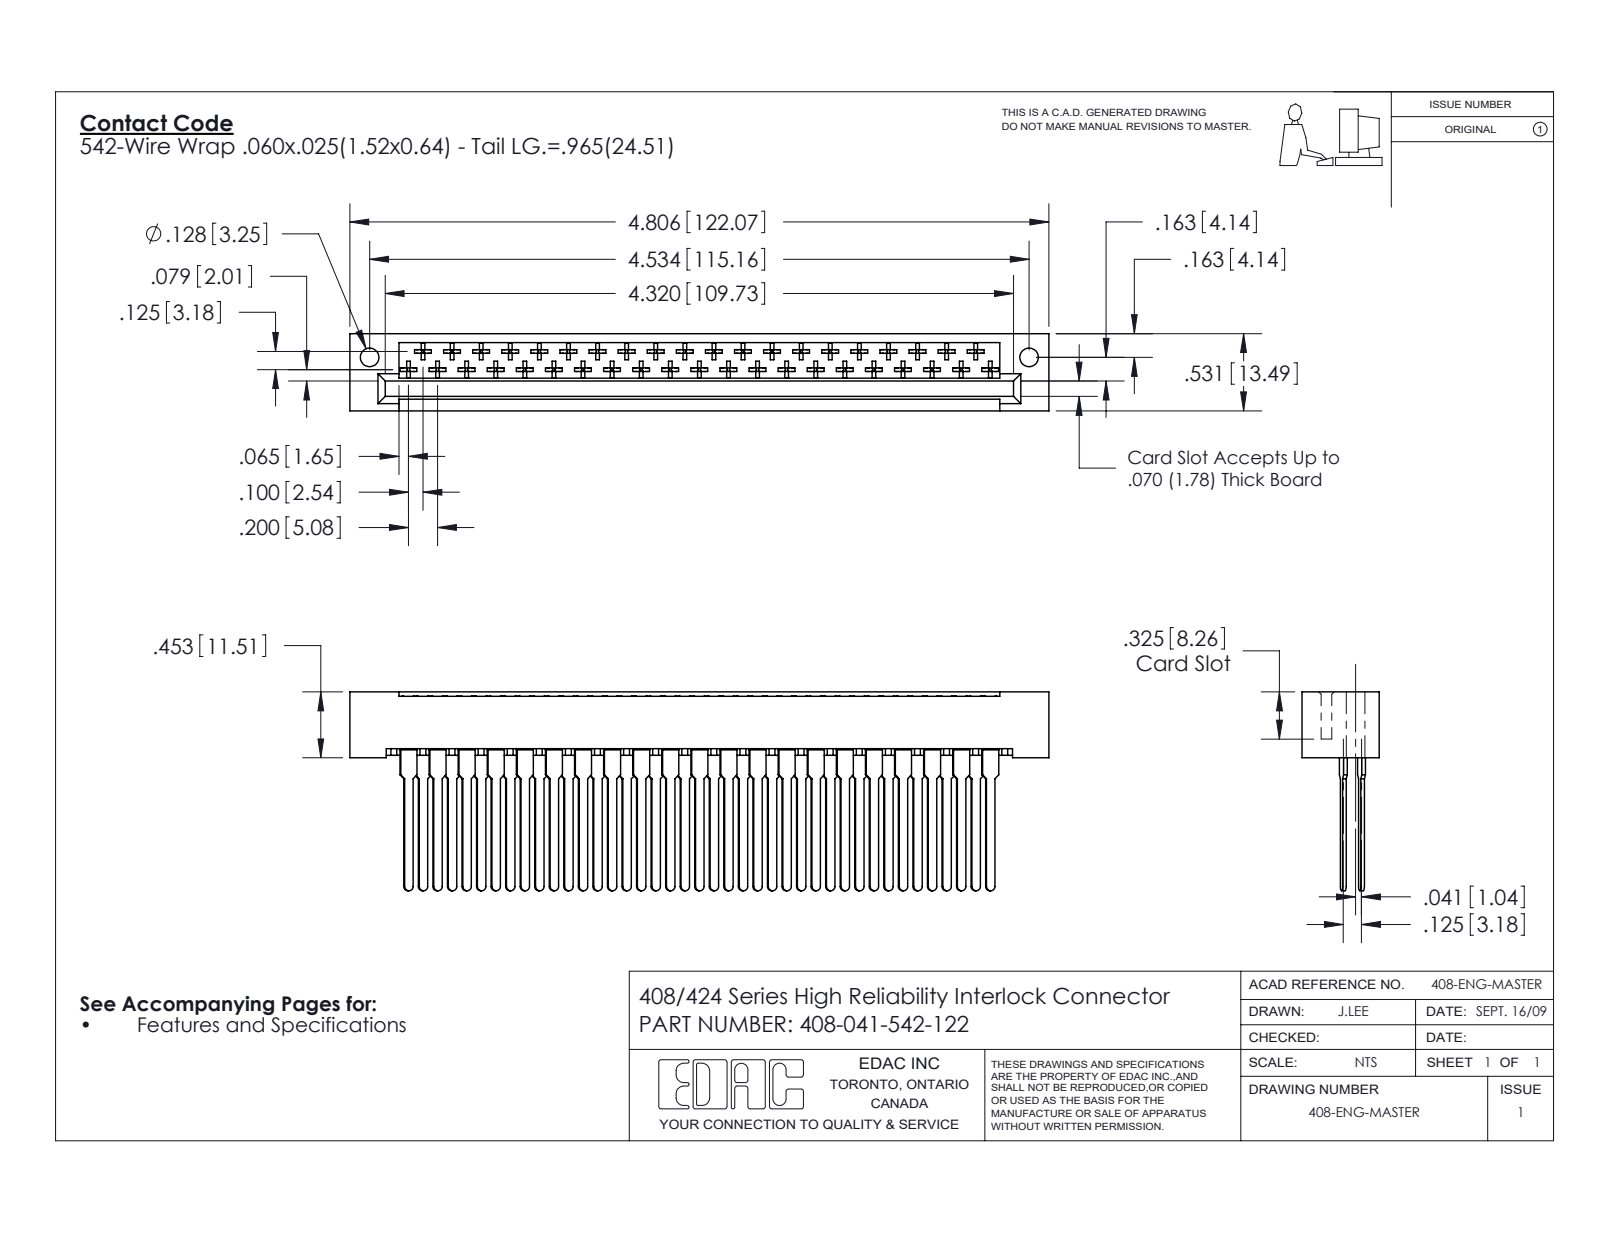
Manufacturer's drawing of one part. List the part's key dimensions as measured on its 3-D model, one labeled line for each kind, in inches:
Part name (STEP PRODUCT): 408-047-542-122; 408-290-001_408-290-142; 408 Part_041 - 1
STEP written by: SolidWorks 2016 (CONFIG_CONTROL_DESIGN)
Units: inches
Bodies: 42 solids, 2217 faces (1676 planar, 377 cylindrical, 164 other)
Overall size (bounding box): 4.806 × 1.367 × 0.531
Volume: 0.867 in³ · Surface area: 31.83 in²
Round holes (diameter × count): ⌀0.128 ×2
Partial cylindrical surfaces — rounded edges, fillets, slot ends (radius × count): R0.01 ×246, R0.02 ×43, R0.03 ×41
Main face-to-face distances: 0.1, 0.296, 0.531, 0.125, 0.025, 0.025, 0.259, 0.272, 0.235, 0.135
Hole centre spacings: 4.534
